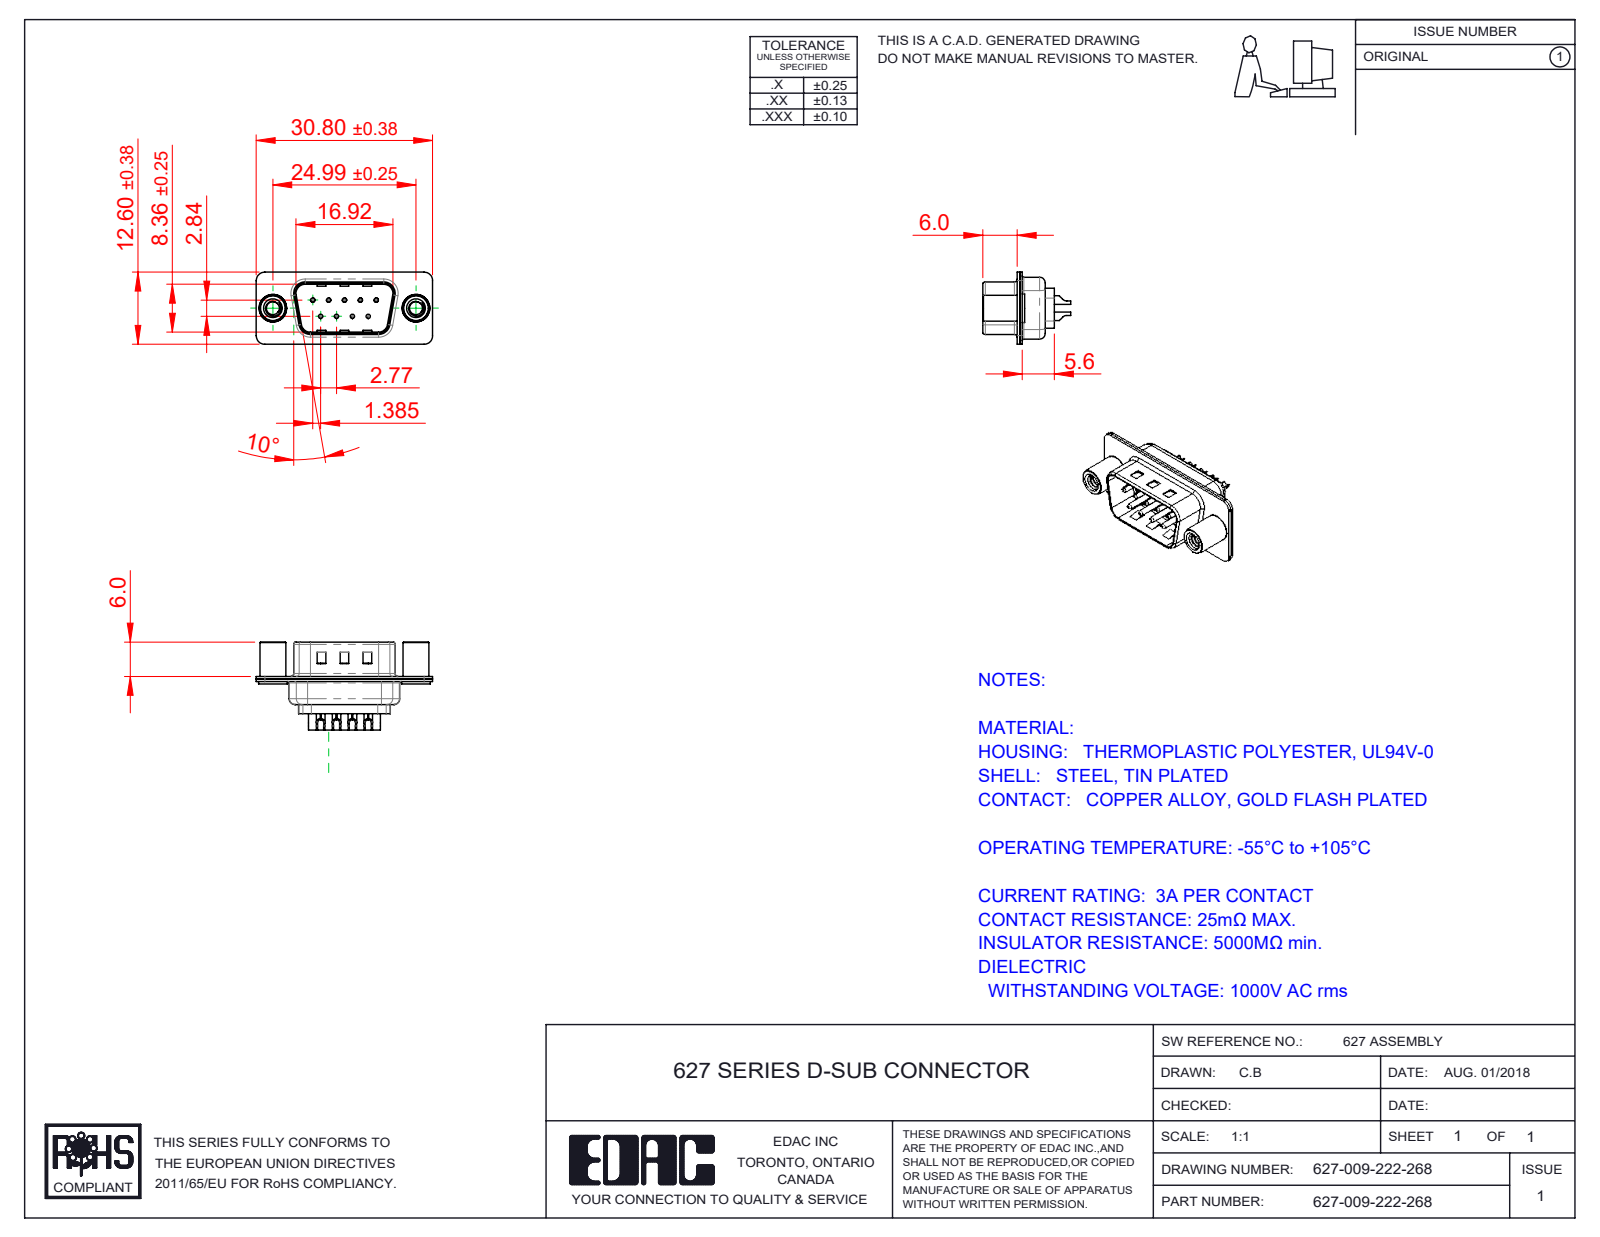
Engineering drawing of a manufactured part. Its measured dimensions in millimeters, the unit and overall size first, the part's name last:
Units: millimetres
Overall size (bounding box): 30.8 × 15.35 × 12.6
Round holes (diameter × count): ⌀0.35 ×9, ⌀1.1 ×9, ⌀1.6 ×9, ⌀2.26 ×2, ⌀4 ×2, ⌀4.8 ×2
Round bosses / shafts (diameter × count): ⌀2 ×9, ⌀1.5 ×9, ⌀0.75 ×9, ⌀5 ×2, ⌀4.9 ×2, ⌀4.5 ×2
Partial cylindrical surfaces — rounded edges, fillets, slot ends (radius × count): R1.5 ×18, R2 ×12, R0.5 ×8, R1.6 ×8, R1 ×6, R0.25 ×4, R0.6 ×4, R0.65 ×4
Main face-to-face distances: 0.4, 0.45, 0.9, 0.82, 9.58, 1.4, 8.76, 0.5, 1.5, 6.5
Hole centre spacings: 3.16, 2.77, 5.54, 5.03, 5.04, 8.31, 7.48, 7.49
Volume: 1 379 mm³ · Surface area: 4 147 mm²
Bodies: 14 solids, 914 faces (235 planar, 418 cylindrical, 261 other)
Part name (STEP PRODUCT): 627 Housing_09 LP; 627 Contact Row 2_22L; 627 Shell Front_09 Contacts; 627 Shell Rear_09 Contacts (+3 more)
STEP written by: SolidWorks 2020 (CONFIG_CONTROL_DESIGN)
